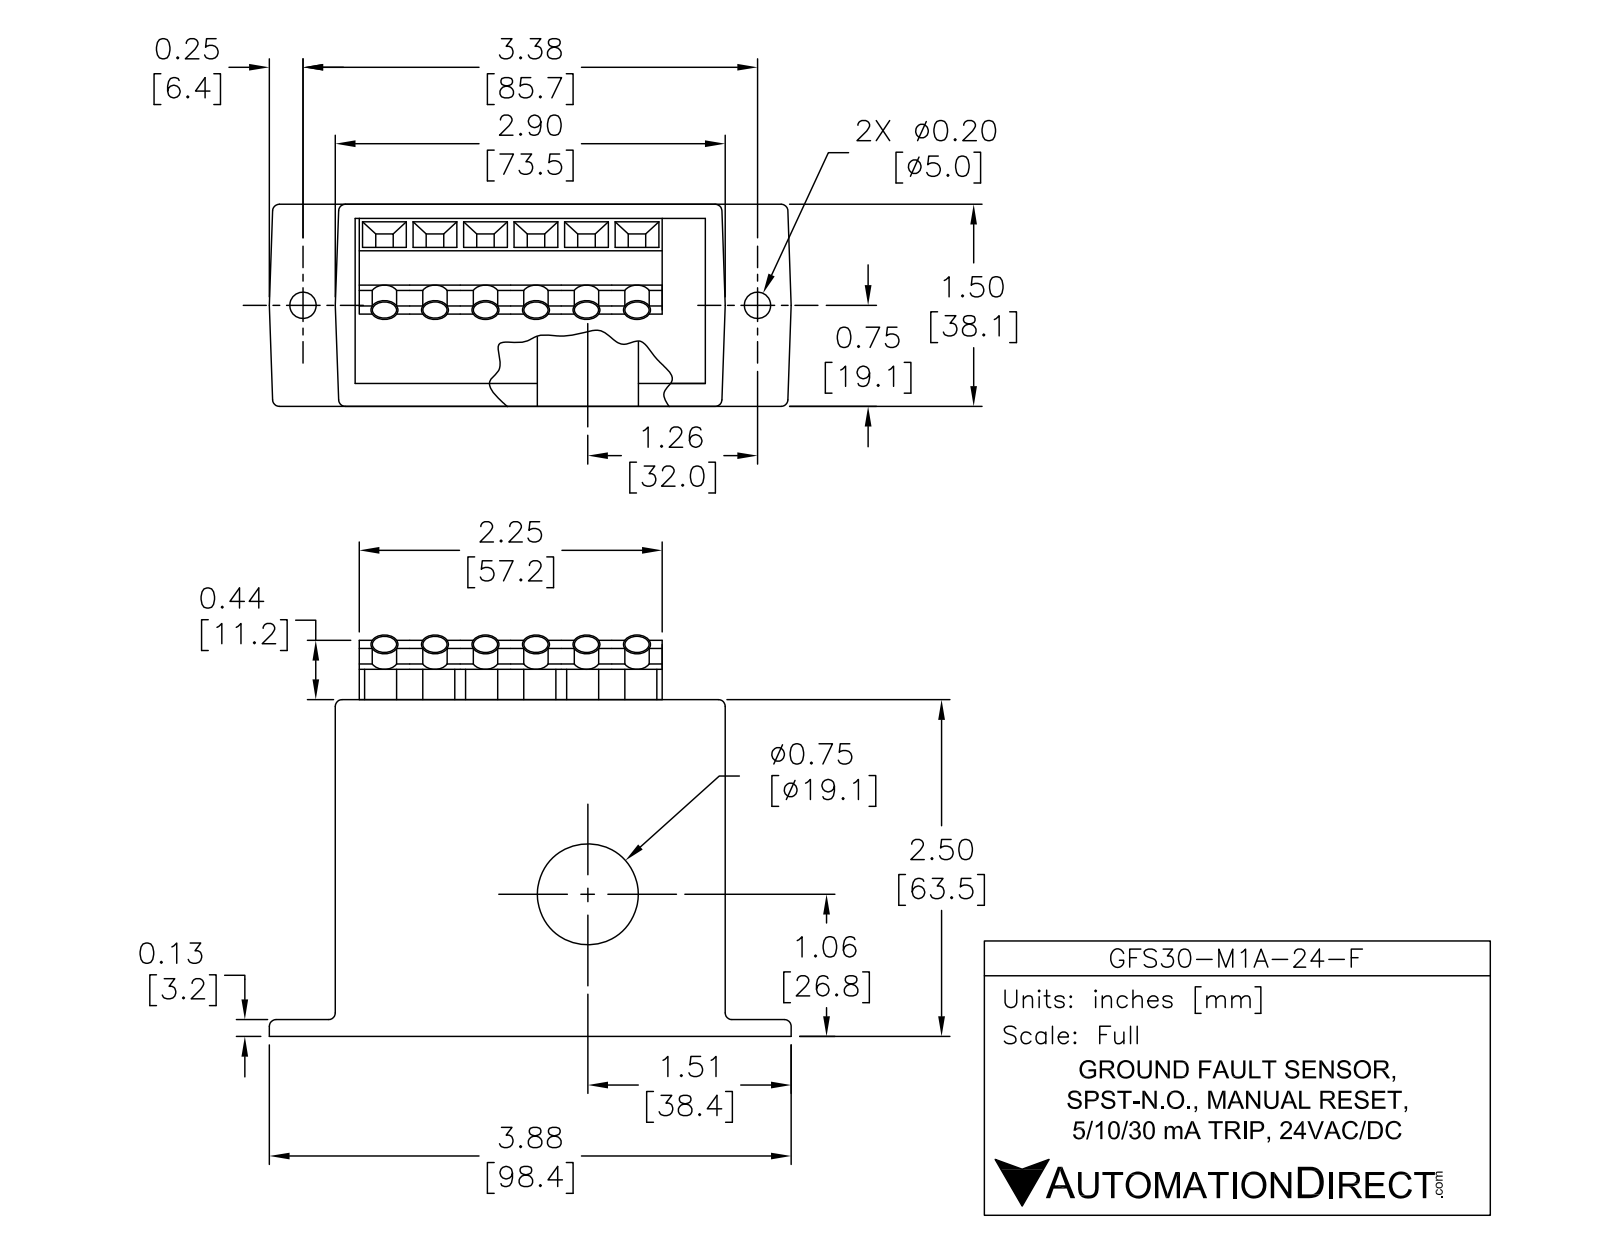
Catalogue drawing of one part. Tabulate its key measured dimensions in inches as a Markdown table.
| quantity | value |
| --- | --- |
| part name | GFS30-M1A-24-F |
| STEP written by | SolidWorks 2019 (AUTOMOTIVE_DESIGN) |
| units | inches |
| bodies | 19 solids, 312 faces (252 planar, 56 cylindrical, 4 other) |
| overall size | 3.875 × 2.908 × 1.504 |
| volume | 10.56 in³ |
| surface area | 54.48 in² |
| round holes (diameter × count) | 0.206 × 6, 0.196 × 2, 0.2 × 2, 0.75 × 1 |
| round bosses / shafts (diameter × count) | 0.186 × 6 |
| partial cylindrical surfaces (radius × count) | 0.128 × 6 |
| main face-to-face distances | 1.5, 2.895, 0.1, 2.455, 2.355, 1.504, 0.104, 2.459, 0.045, 2.334 |
| hole center spacings | 0.748, 0.354, 0.394, 0.37, 0.374, 0.681, 0.768, 1.022 |
